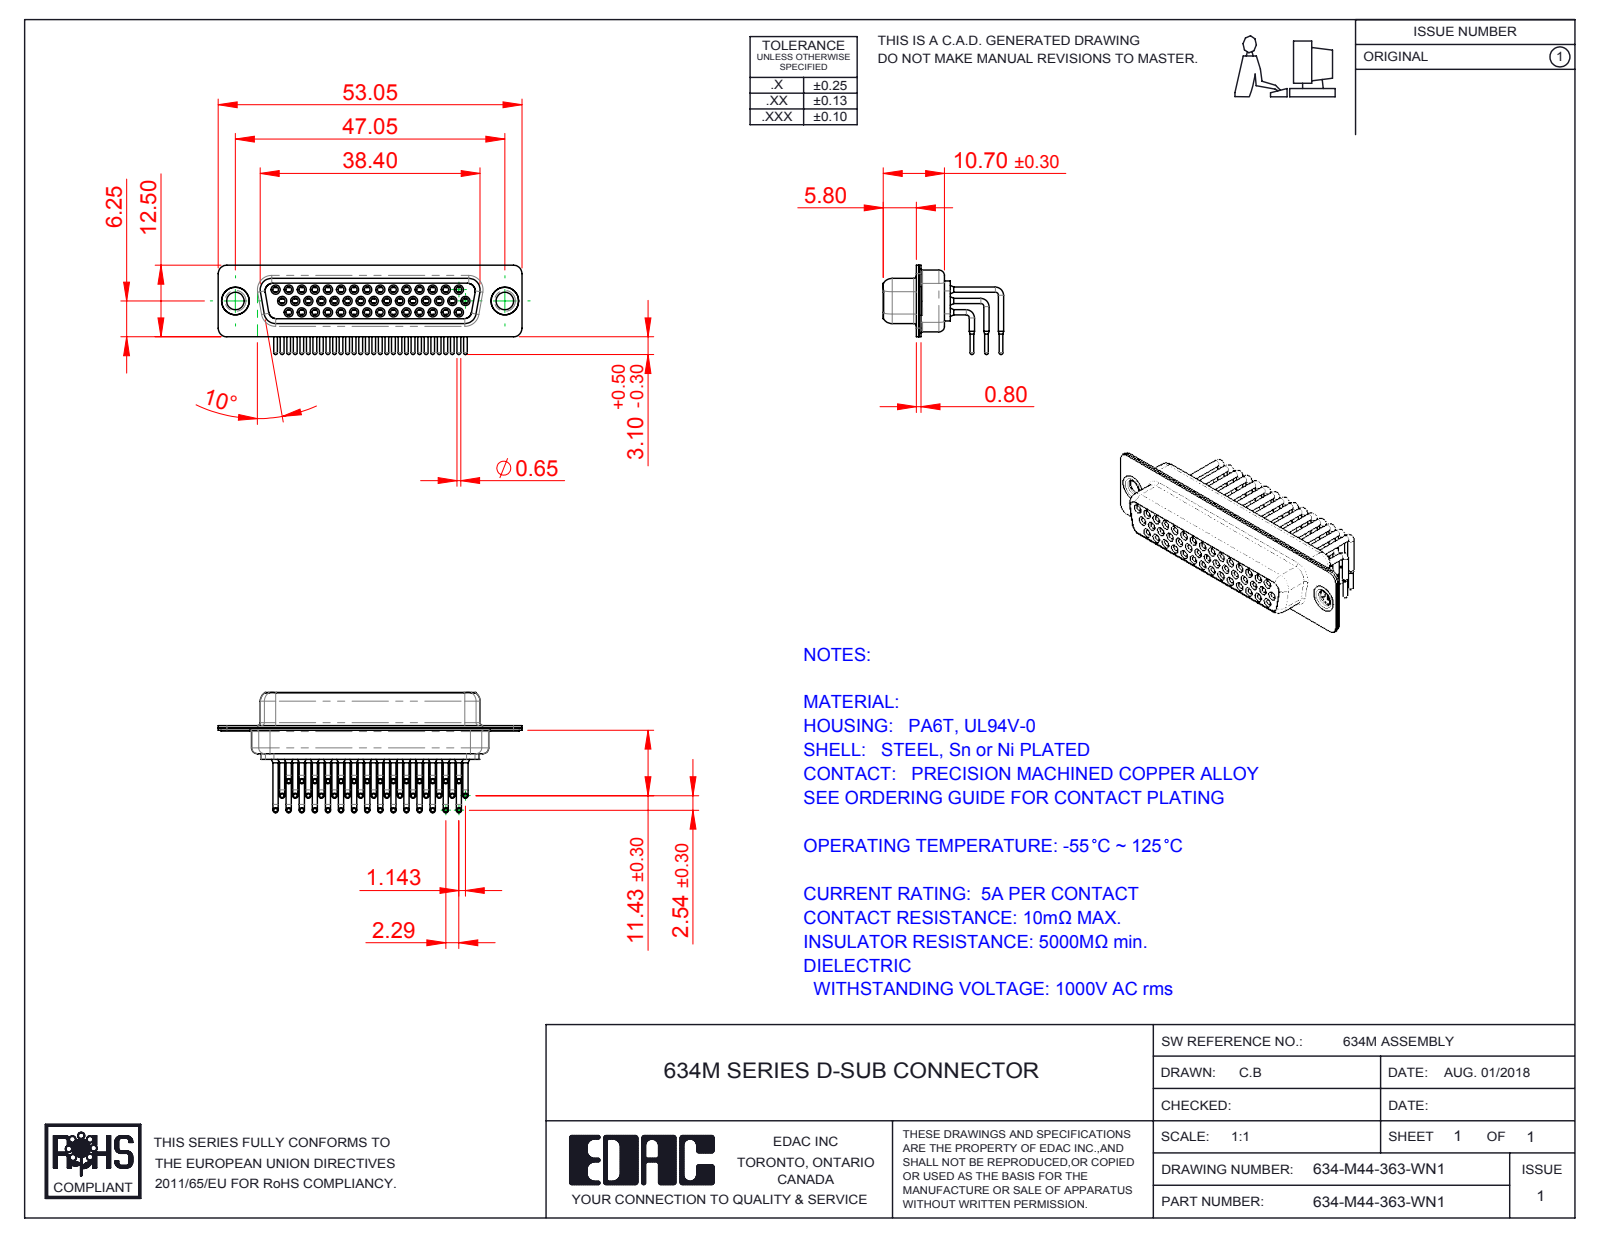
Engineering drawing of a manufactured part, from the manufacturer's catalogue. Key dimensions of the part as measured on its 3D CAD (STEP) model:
Part name (STEP PRODUCT): 634M Contact Row 1; 634M Thru Hole Rivet; 634M Shell Rear_44 Contacts; 634-M44-363-WN1 (+4 more)
STEP written by: SolidWorks 2016 (CONFIG_CONTROL_DESIGN)
Units: millimetres
Bodies: 49 solids, 2585 faces (727 planar, 1133 cylindrical, 725 other)
Overall size (bounding box): 53.05 × 21.02 × 15.6
Volume: 3 758 mm³ · Surface area: 12 888 mm²
Round holes (diameter × count): ⌀1 ×44, ⌀1.1 ×44, ⌀1.7 ×44, ⌀1.8 ×44, ⌀2 ×44, ⌀3.05 ×2, ⌀4 ×2, ⌀4.8 ×2
Round bosses / shafts (diameter × count): ⌀0.9 ×88, ⌀1.6 ×44, ⌀1.5 ×44, ⌀0.65 ×44, ⌀5 ×2, ⌀4.9 ×2, ⌀3.55 ×2
Partial cylindrical surfaces — rounded edges, fillets, slot ends (radius × count): R1.5 ×16, R2 ×12, R1.35 ×8, R1.6 ×8, R0.25 ×4, R0.5 ×4, R0.6 ×4, R0.65 ×4
Main face-to-face distances: 0.4, 1.45, 8.95, 1.9, 8.5, 2.3, 6.2, 7.05, 0.45, 0.85
Hole centre spacings: 2.28, 3.96, 2.29, 4.57, 8.24, 6.86, 11.43, 10.48
